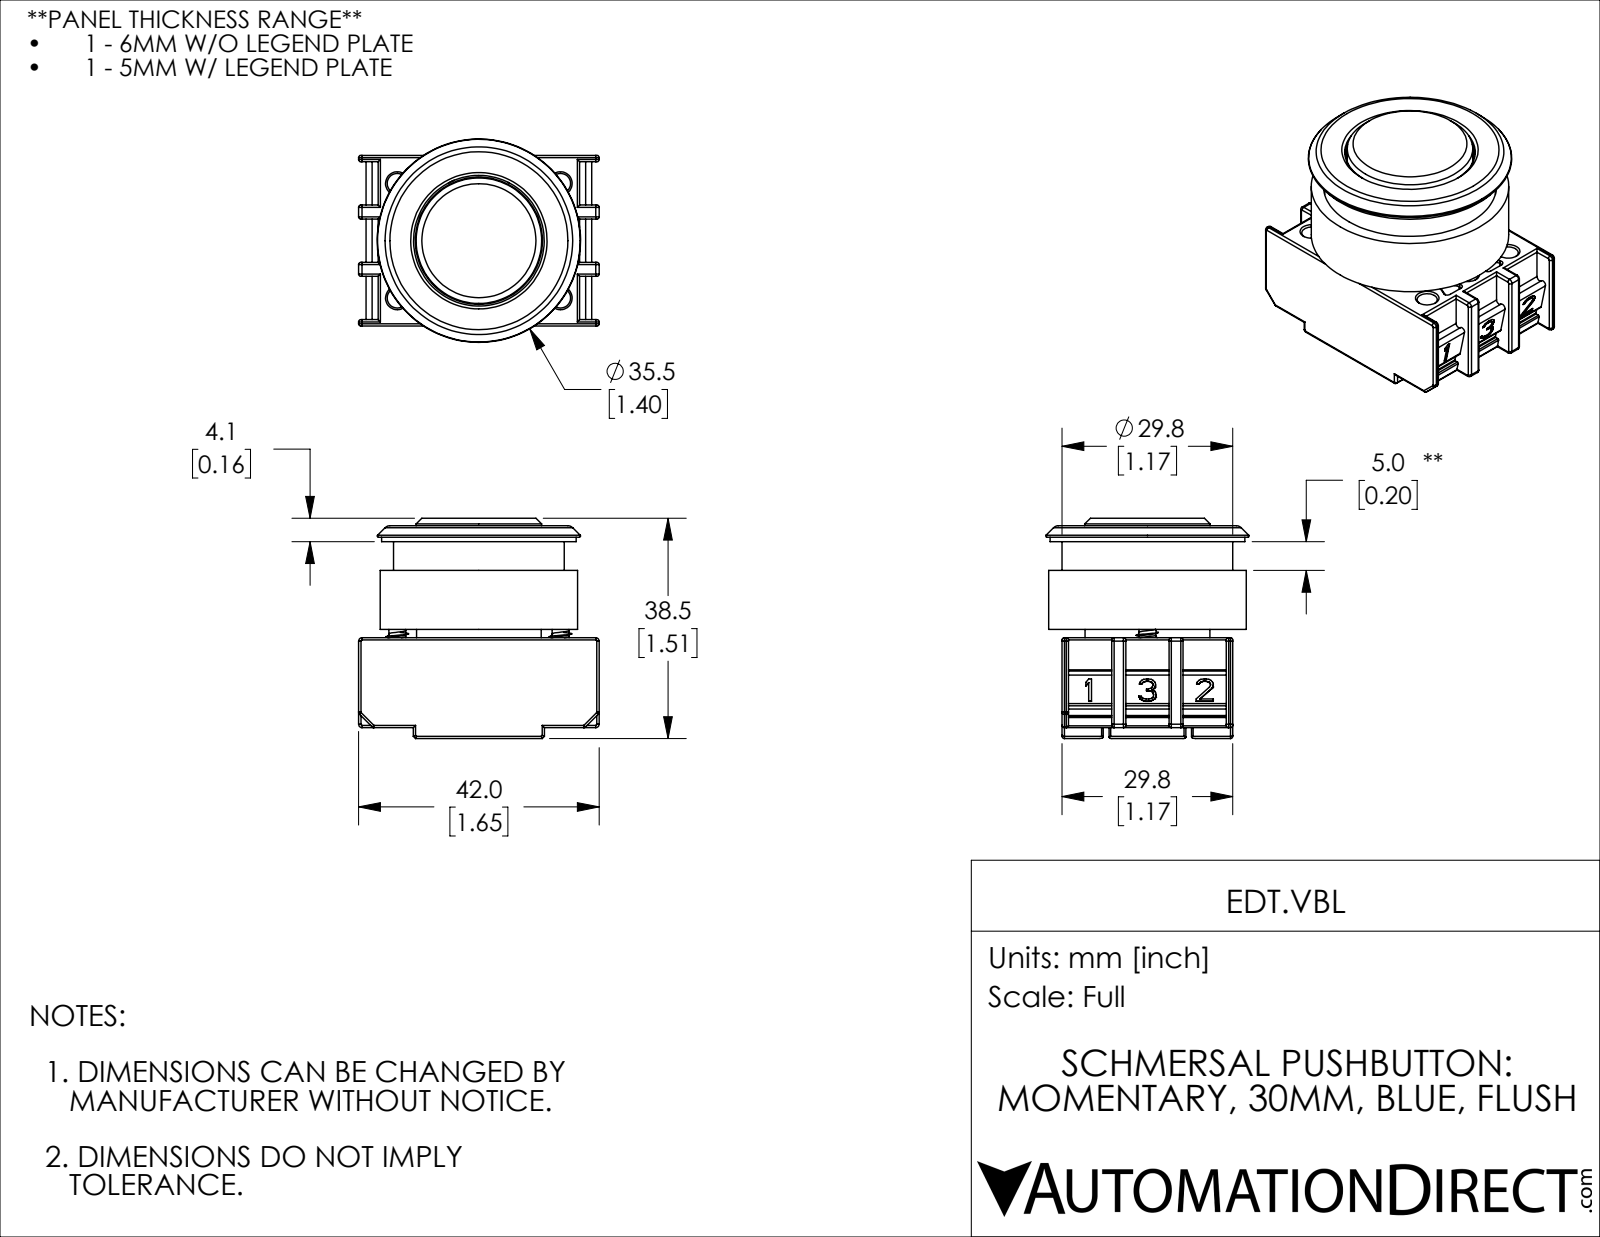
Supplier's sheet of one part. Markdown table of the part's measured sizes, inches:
| quantity | value |
| --- | --- |
| part name | EDT.VBL |
| STEP written by | SolidWorks 2019 (CONFIG_CONTROL_DESIGN) |
| units | inches |
| bodies | 3 solids, 1361 faces (509 planar, 460 cylindrical, 392 other) |
| overall size | 1.654 × 1.514 × 1.398 |
| volume | 1.379 in³ |
| surface area | 31.76 in² |
| round holes (diameter × count) | 0.138 × 6, 0.203 × 6, 0.161 × 1, 0.492 × 1, 0.709 × 1, 0.756 × 1, 0.874 × 1, 0.898 × 1, 0.953 × 1, 1.024 × 1, 1.063 × 1, 1.189 × 1 |
| round bosses / shafts (diameter × count) | 0.189 × 2, 0.115 × 2, 1.358 × 1, 1.339 × 1, 1.173 × 1, 0.969 × 1, 0.862 × 1, 0.858 × 1 |
| partial cylindrical surfaces (radius × count) | 0.016 × 112, 0.012 × 48, 0.008 × 24, 0.024 × 8, 0.02 × 6, 0.004 × 2, 0.024 × 2, 0.031 × 2 |
| main face-to-face distances | 1.173, 0.075, 0.764, 0.232, 0.161, 0.057, 0.638, 0.75, 0.394, 0.051 |
| hole center spacings | 0.394, 0.685, 1.189, 1.122, 0.561, 0.787, 1.371 |
